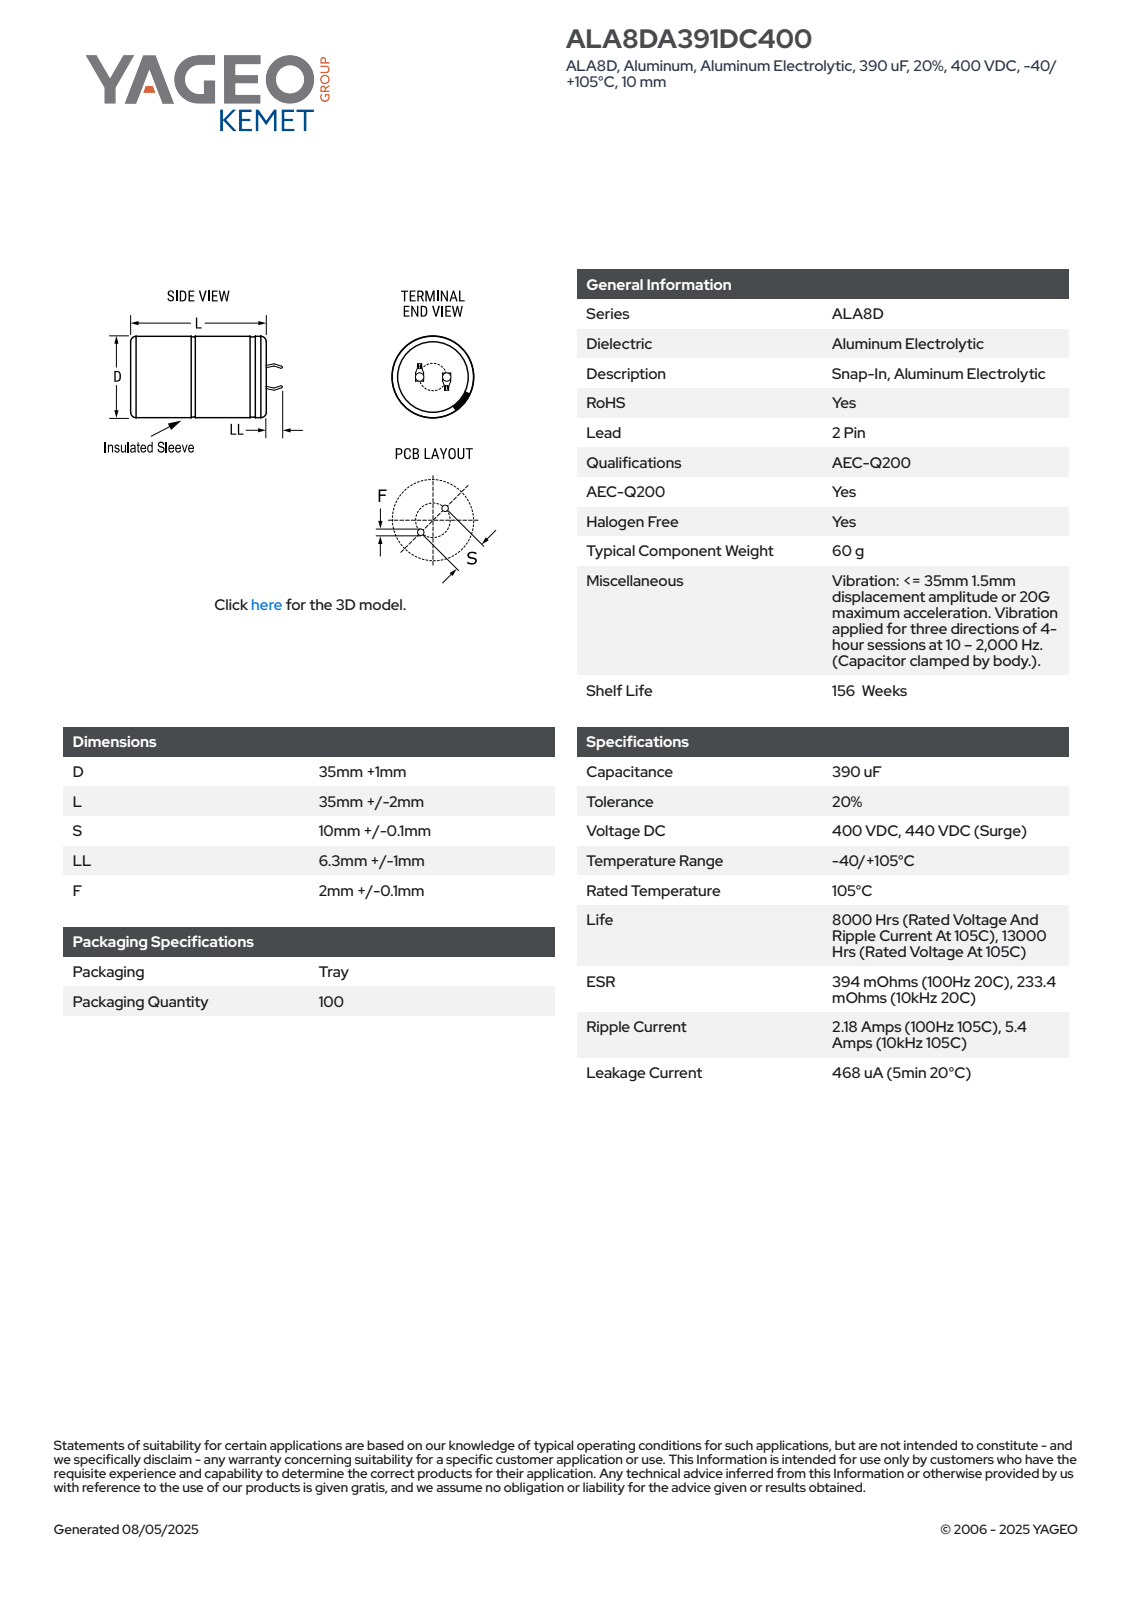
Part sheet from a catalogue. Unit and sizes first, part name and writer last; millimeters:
Units: millimetres
Overall size (bounding box): 44.29 × 36 × 36
Round holes (diameter × count): ⌀31.85 ×1
Round bosses / shafts (diameter × count): ⌀36 ×1
Partial cylindrical surfaces — rounded edges, fillets, slot ends (radius × count): R17.99 ×1
Main face-to-face distances: 36.99, 0.6, 37.49, 0.5, 7.08, 7.64, 1.35, 0.75, 7.68, 6.48
Volume: 37 090 mm³ · Surface area: 6 279 mm²
Bodies: 1 solid, 106 faces (52 planar, 11 cylindrical, 43 other)
Part name (STEP PRODUCT): CARS_K2PAV_35X35_D36L37S10LL7.3F2.1
STEP written by: SolidWorks 2021 (AUTOMOTIVE_DESIGN)
